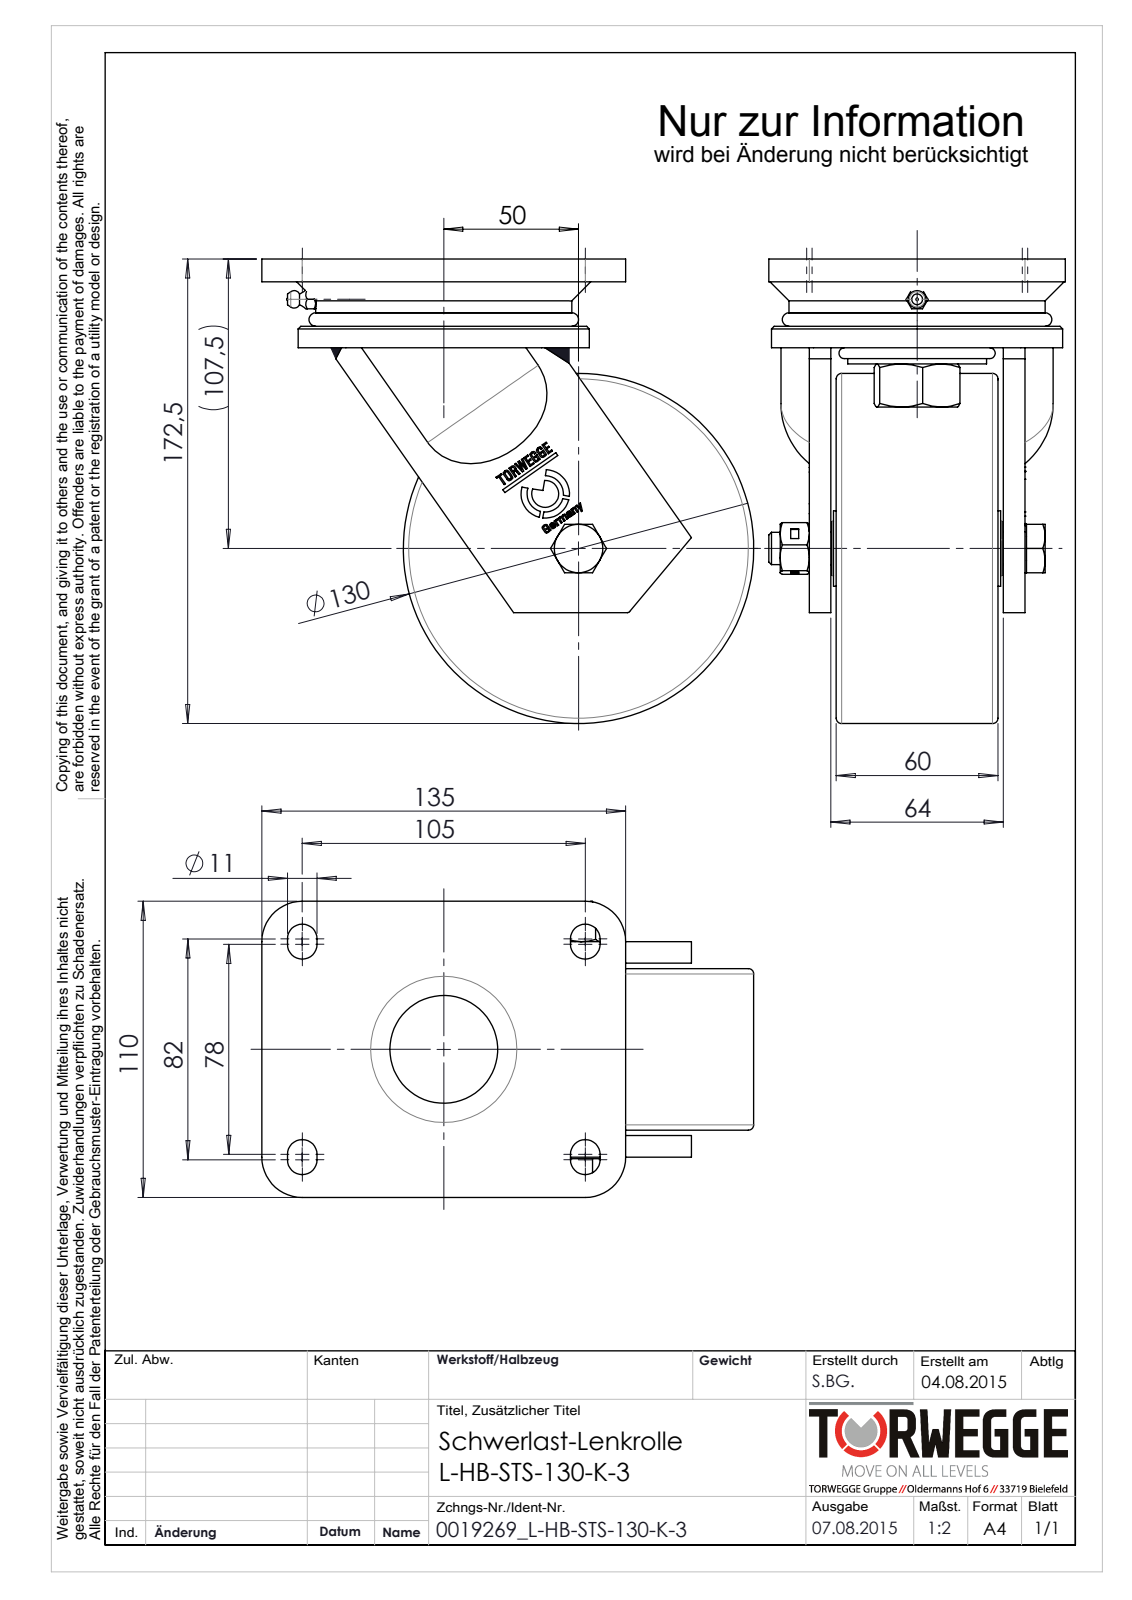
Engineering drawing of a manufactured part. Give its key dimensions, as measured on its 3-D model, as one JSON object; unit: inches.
{"part_name": "0019269_L-HB-STS-130-K-3", "step_written_by": "SolidWorks 2014 (AUTOMOTIVE_DESIGN)", "units": "inches", "bodies": {"solids": 24, "faces": 864, "planar": 395, "cylindrical": 134, "other": 335}, "overall_size": [7.185, 6.791, 4.331], "volume_in3": 74.39, "surface_area_in2": 331.7, "round_holes": [[0.787, 2], [0.236, 1], [0.394, 1], [0.402, 1], [0.472, 1], [0.48, 1], [0.492, 1], [0.681, 1], [0.984, 1], [1.106, 1], [1.531, 1], [1.575, 1]], "round_bosses_or_shafts": [[5.118, 1], [4.252, 1], [2.028, 1], [1.102, 1], [0.779, 1], [0.709, 1]], "partial_cylinders_radius": [[0.217, 8], [0.394, 4], [0.591, 4], [1.063, 2], [1.378, 2], [0.039, 1], [0.266, 1], [0.354, 1]], "face_to_face_distances": [0.079, 0.315, 0.394, 2.362, 2.835, 2.441, 2.756, 0.984, 0.335, 1.299], "hole_center_spacings": [0.935]}
